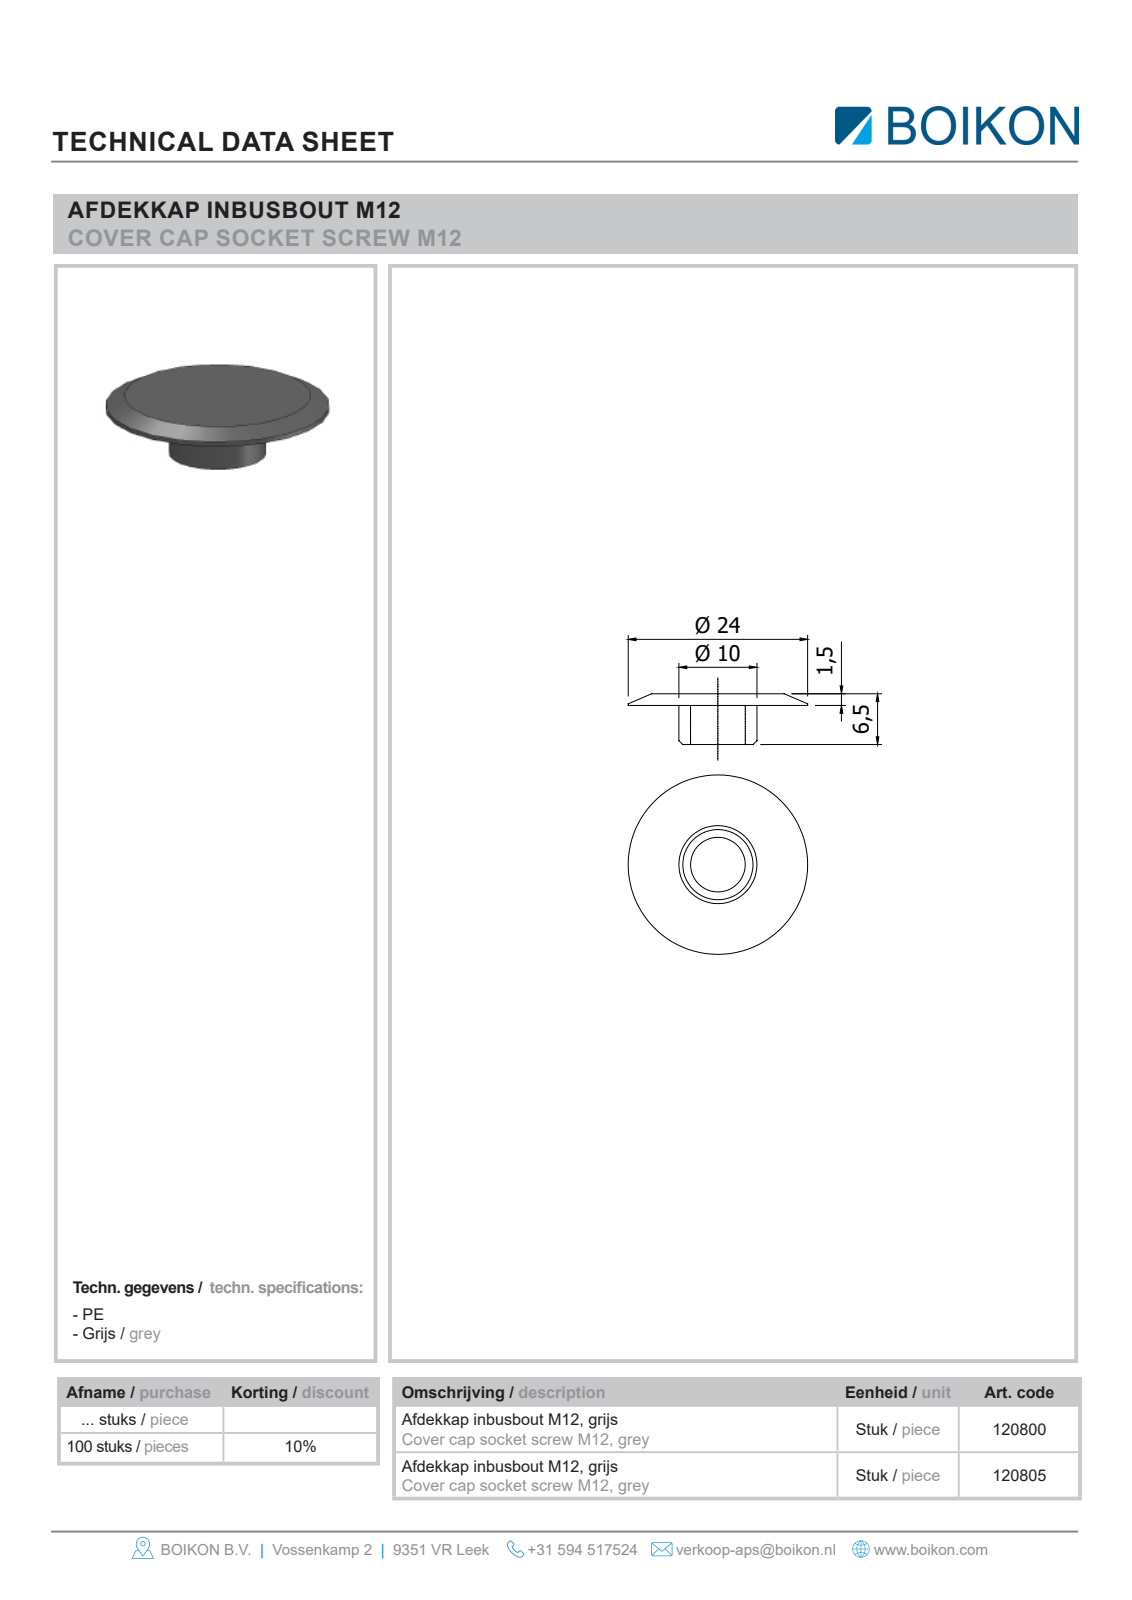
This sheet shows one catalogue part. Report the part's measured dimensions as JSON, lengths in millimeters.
{"part_name": "Root; 120800Afdekkap voor inbus zwartBOIKON", "step_written_by": "HiCAD 2013 1802.4 Build 509 (AUTOMOTIVE_DESIGN)", "units": "millimeters", "bodies": {"solids": 1, "faces": 8, "planar": 4, "cylindrical": 3, "other": 1}, "overall_size": [24, 24, 6.5], "volume_mm3": 817, "surface_area_mm2": 1238, "round_holes": [[7.4, 1]], "round_bosses_or_shafts": [[24, 1], [10.4, 1]], "face_to_face_distances": [1.5, 5, 6.5]}
